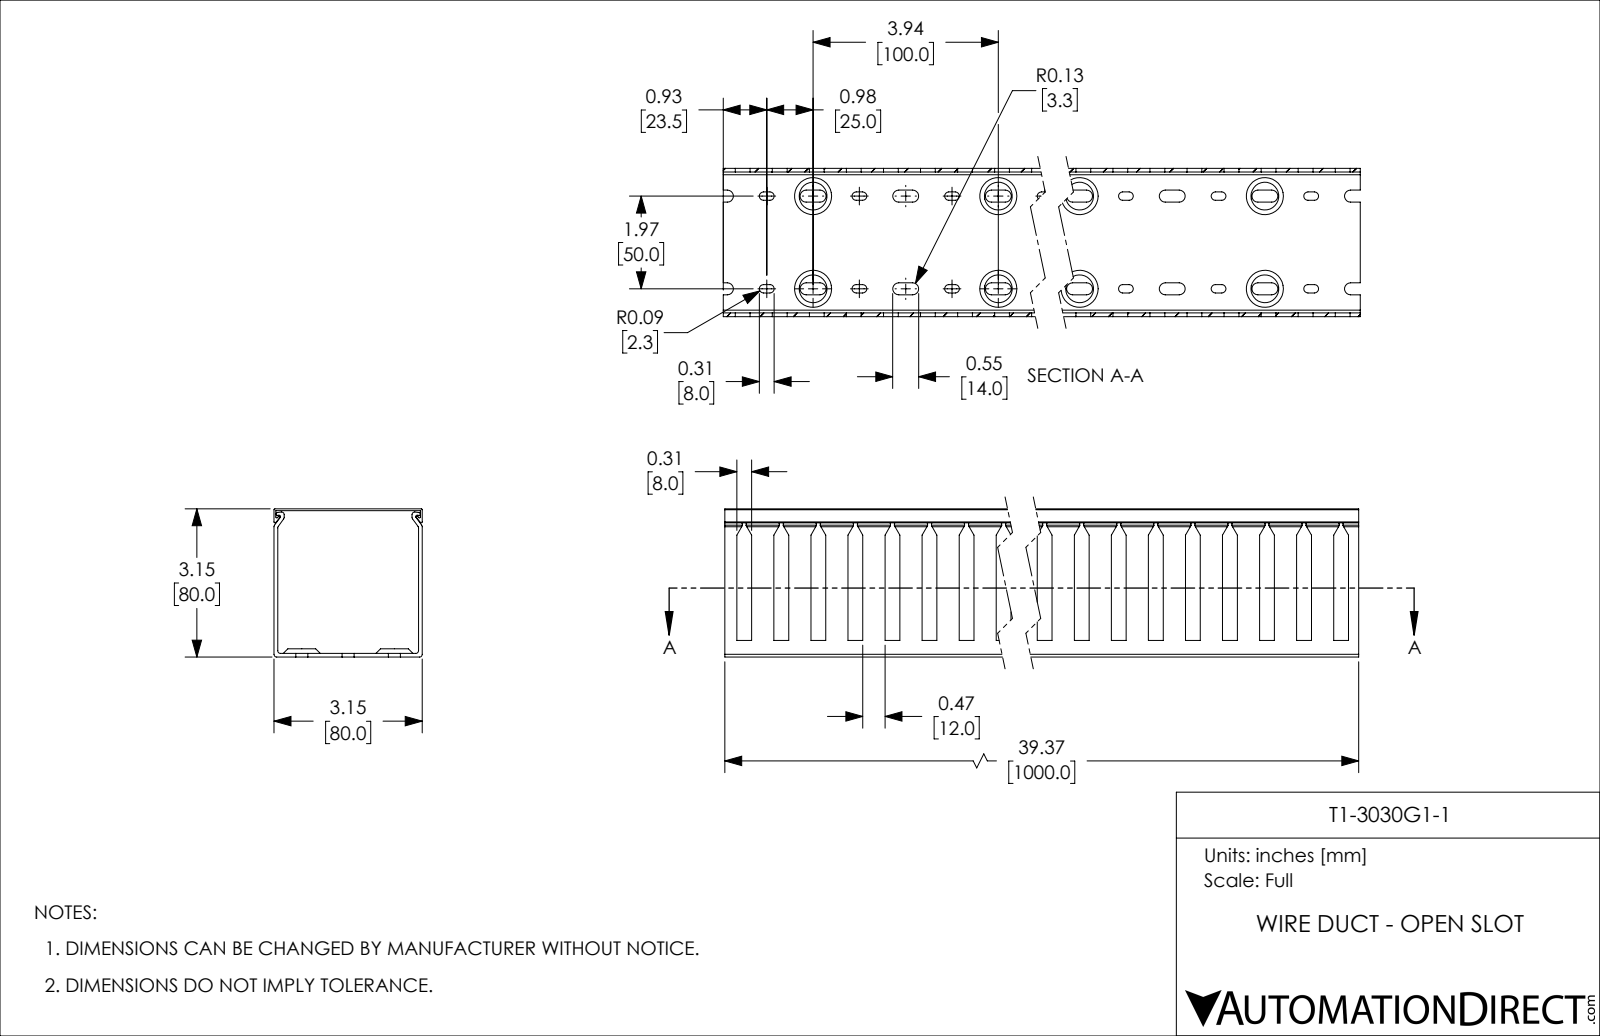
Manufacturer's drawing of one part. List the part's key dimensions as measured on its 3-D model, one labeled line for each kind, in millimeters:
Part name (STEP PRODUCT): T1-3030G1-1
STEP written by: SolidWorks 2021 (CONFIG_CONTROL_DESIGN)
Units: millimetres
Bodies: 2 solids, 1063 faces (562 planar, 461 cylindrical, 40 other)
Overall size (bounding box): 1000 × 80 × 80
Volume: 551 284 mm³ · Surface area: 654 594 mm²
Partial cylindrical surfaces — rounded edges, fillets, slot ends (radius × count): R3.25 ×100, R2.25 ×80, R1.5 ×12, R0.5 ×8, R0.75 ×6
Main face-to-face distances: 2, 78, 80, 1, 79, 77, 76, 4.5, 74.5, 20
